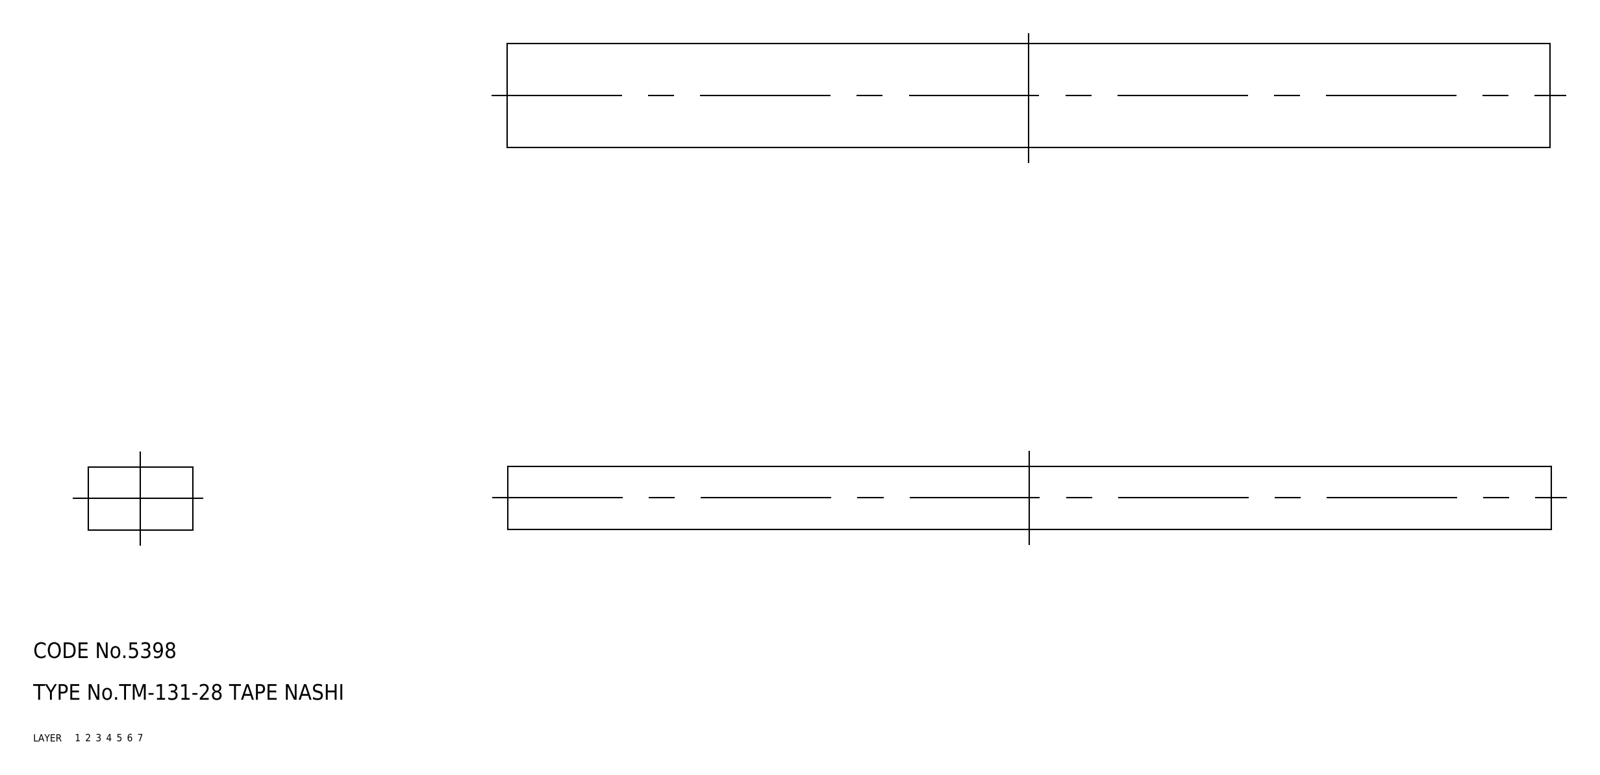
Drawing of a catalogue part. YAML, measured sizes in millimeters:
part_name: "rubber foam"
step_written_by: "CADfix (AUTOMOTIVE_DESIGN)"
units: millimeters
bodies: {solids: 1, faces: 6, planar: 0, cylindrical: 0, other: 6}
overall_size: [200, 20, 12]
volume: 48000
surface_area: 13280
